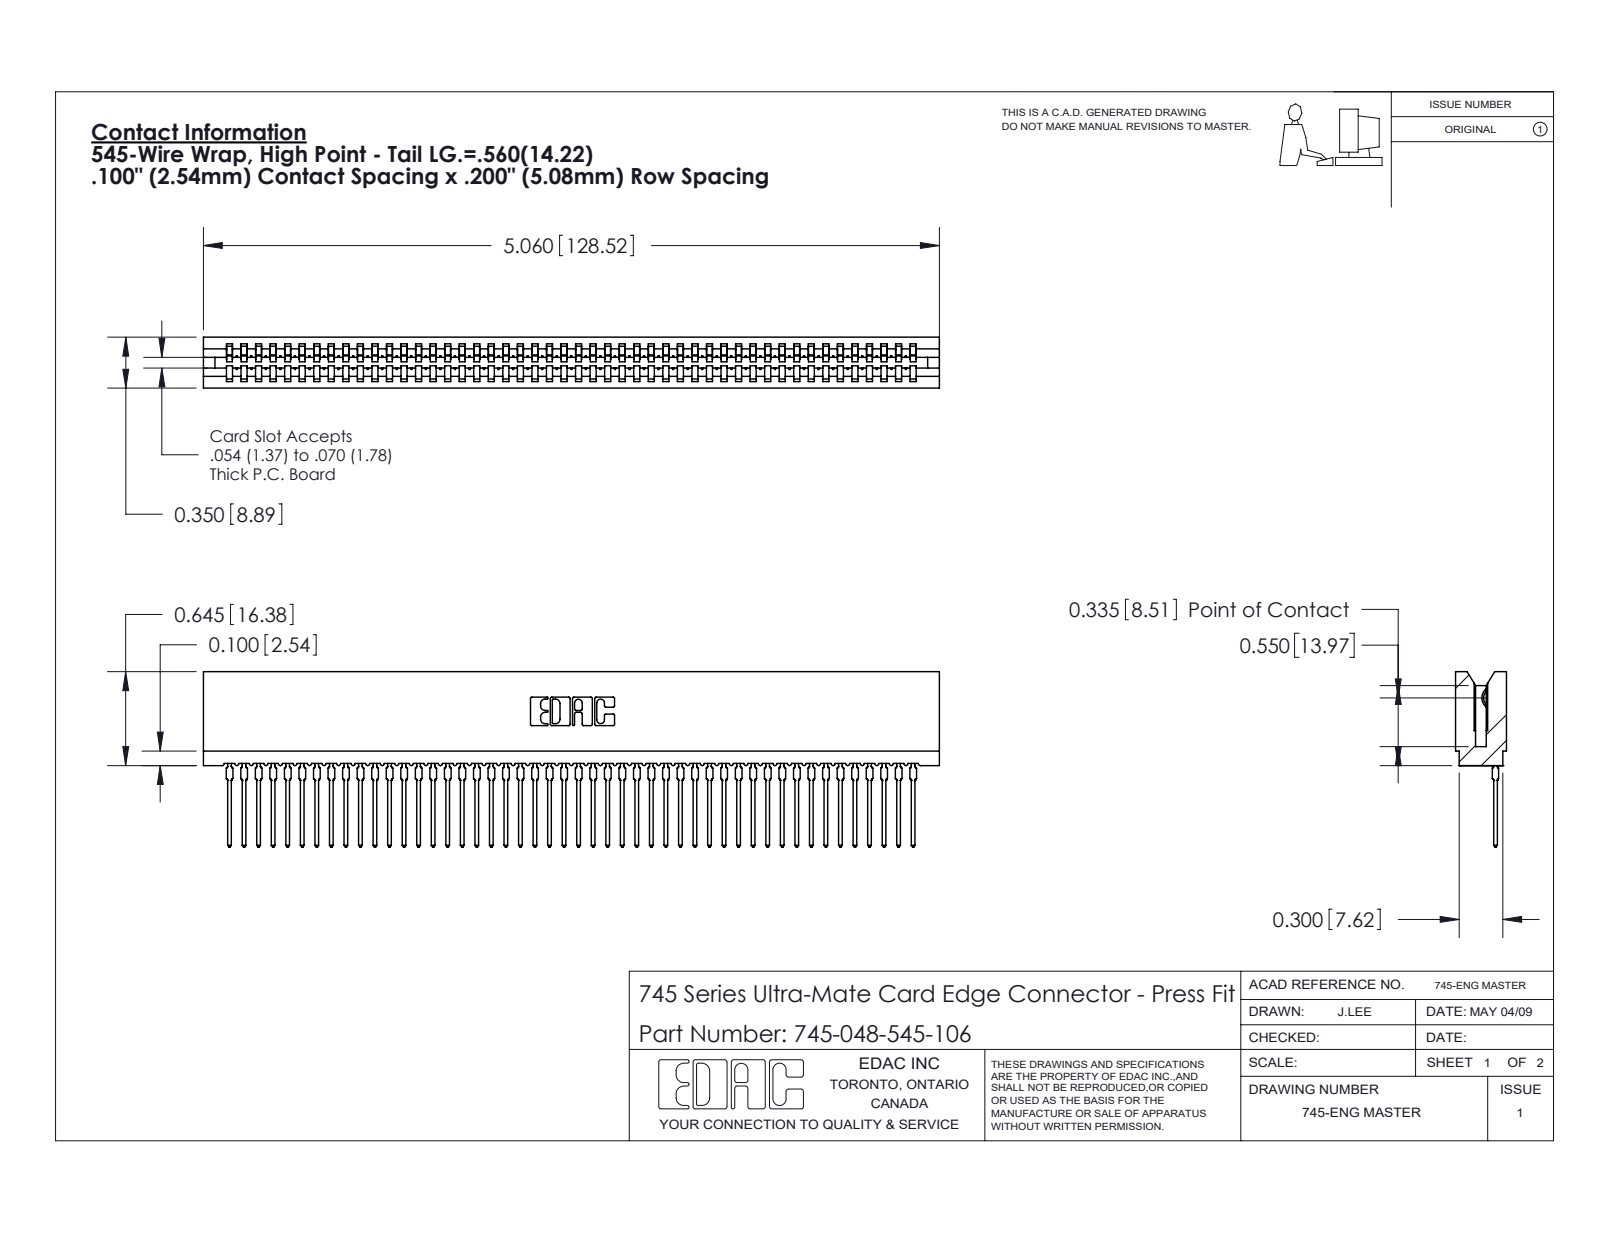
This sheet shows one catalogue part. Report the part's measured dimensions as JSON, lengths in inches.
{"part_name": "745 Part_Insulator Option - 06; 745-048-545-106; 745-292-001_545", "step_written_by": "SolidWorks 2020 (CONFIG_CONTROL_DESIGN)", "units": "inches", "bodies": {"solids": 49, "faces": 5472, "planar": 3272, "cylindrical": 952, "other": 1248}, "overall_size": [5.06, 1.206, 0.35], "volume_in3": 0.684, "surface_area_in2": 33.71, "partial_cylinders_radius": [[0.015, 96], [0.021, 96], [0.01, 22], [0.007, 6], [0.031, 6], [0.005, 4], [0.011, 4], [0.026, 3]], "face_to_face_distances": [0.35, 0.045, 0.305, 0.138, 0.212, 0.093, 0.167, 0.063, 0.287, 0.243]}
